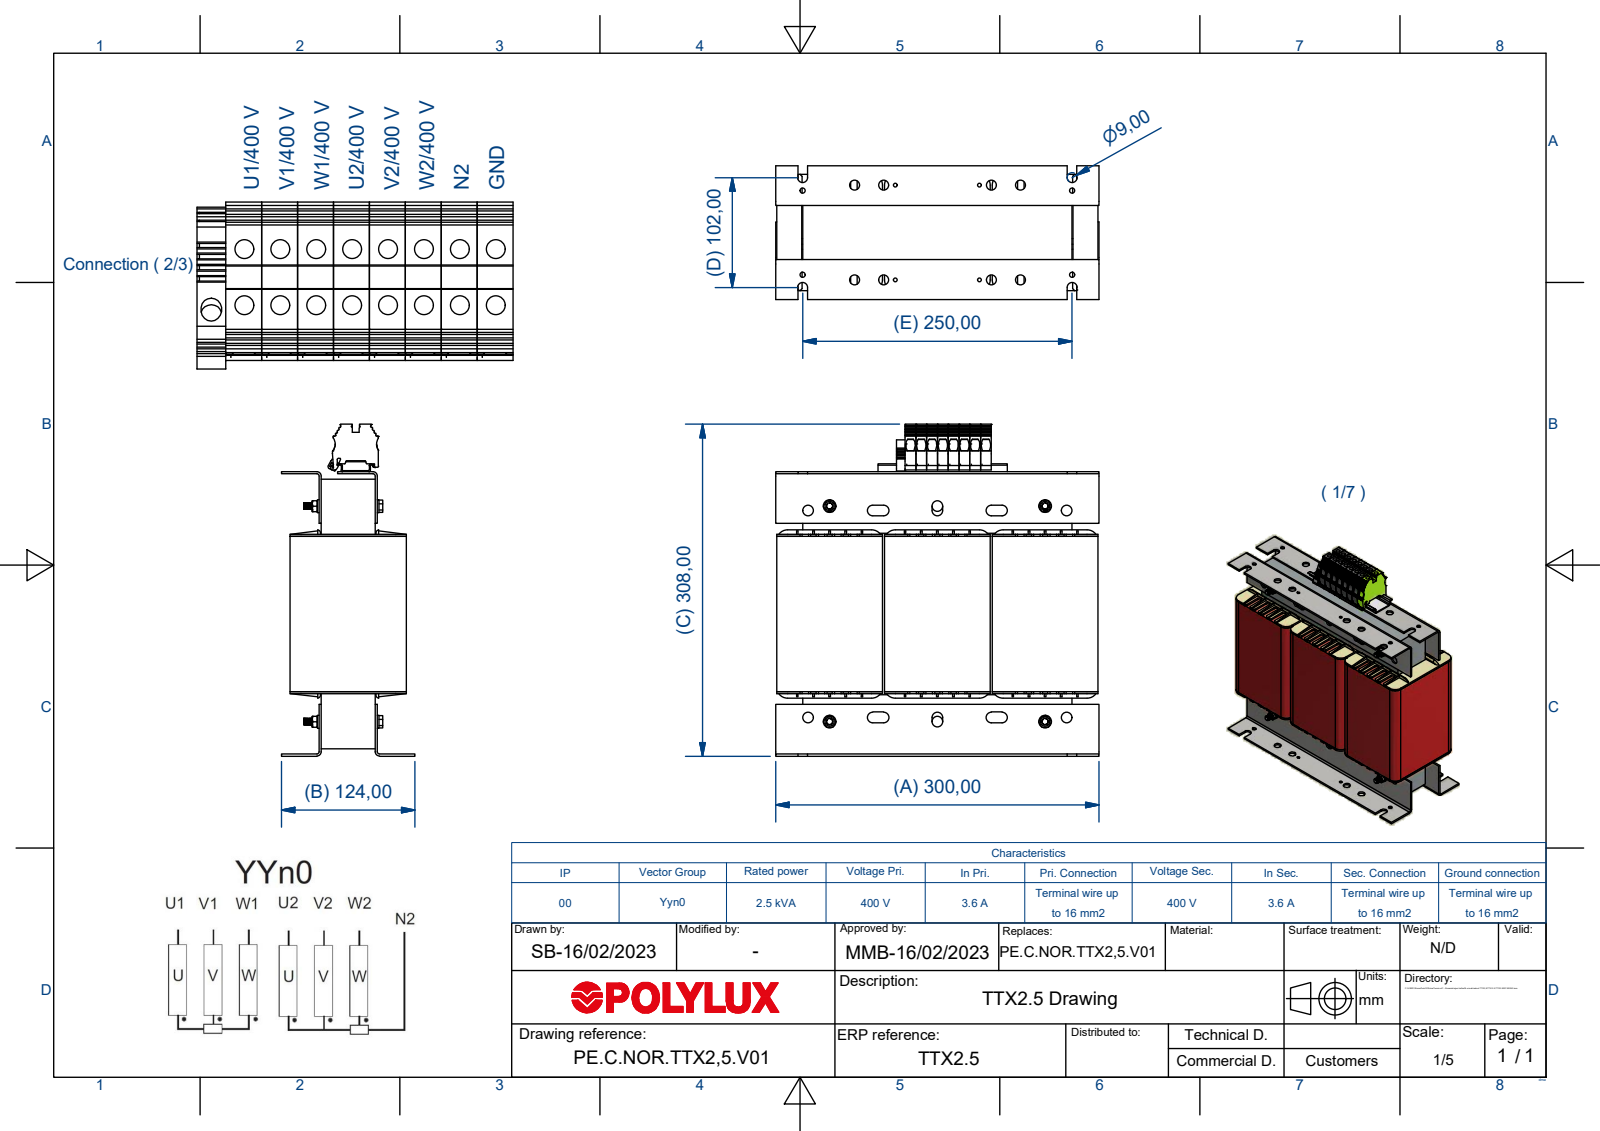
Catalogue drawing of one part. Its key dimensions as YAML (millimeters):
part_name: "TTX2.5; Núcleo RC50x50; BRI50-3IP0E25; DIN 934 - M6 x 1 (+8 more)"
step_written_by: "Autodesk Inventor 2018 (AUTOMOTIVE_DESIGN)"
units: millimeters
bodies: {solids: 38, faces: 2672, planar: 1898, cylindrical: 726, other: 48}
overall_size: [308.11, 300, 124]
volume: 6145000
surface_area: 1057000
round_holes:
  - {diameter: 5.3, count: 16}
  - {diameter: 9, count: 12}
  - {diameter: 4.92, count: 10}
  - {diameter: 10, count: 10}
  - {diameter: 3.5, count: 6}
  - {diameter: 6.4, count: 4}
  - {diameter: 3, count: 2}
  - {diameter: 5.8, count: 2}
round_bosses_or_shafts:
  - {diameter: 12, count: 4}
  - {diameter: 6, count: 4}
partial_cylinders:
  - {radius: 0.5, count: 33}
  - {radius: 3, count: 28}
  - {radius: 11, count: 18}
  - {radius: 10, count: 16}
  - {radius: 1, count: 12}
  - {radius: 0.3, count: 10}
  - {radius: 5, count: 10}
  - {radius: 0.1, count: 9}
face_to_face_distances: [2, 52, 100, 54, 76, 1.25, 52.75, 200, 50, 22]
hole_center_spacings: [52, 100, 11, 27, 36, 38, 48.26, 75.17]
